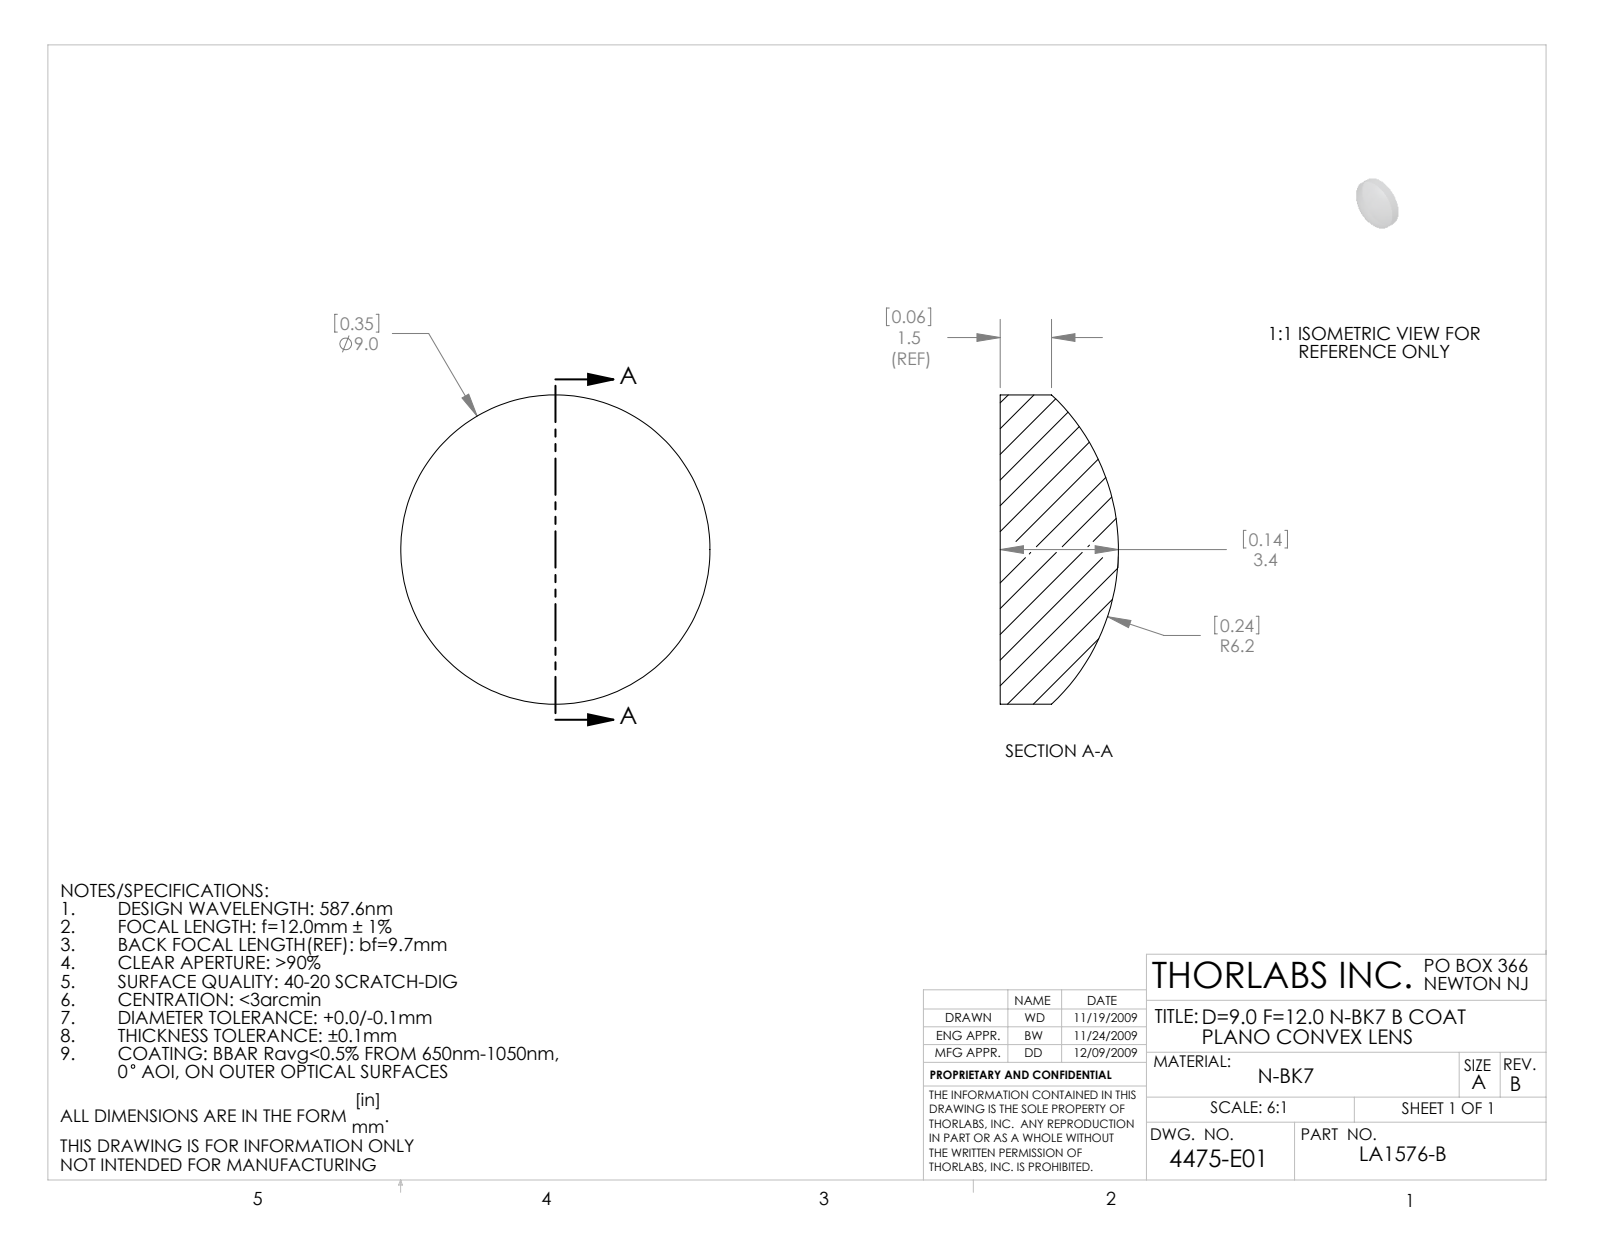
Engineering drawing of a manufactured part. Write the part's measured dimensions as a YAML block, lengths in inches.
part_name: "4475-E0W"
step_written_by: "SolidWorks 2009 (AUTOMOTIVE_DESIGN)"
units: inches
bodies: {solids: 1, faces: 5, planar: 1, cylindrical: 2, other: 2}
overall_size: [0.354, 0.354, 0.135]
volume: 0.01
surface_area: 0.281
round_bosses_or_shafts:
  - {diameter: 0.354, count: 1}
